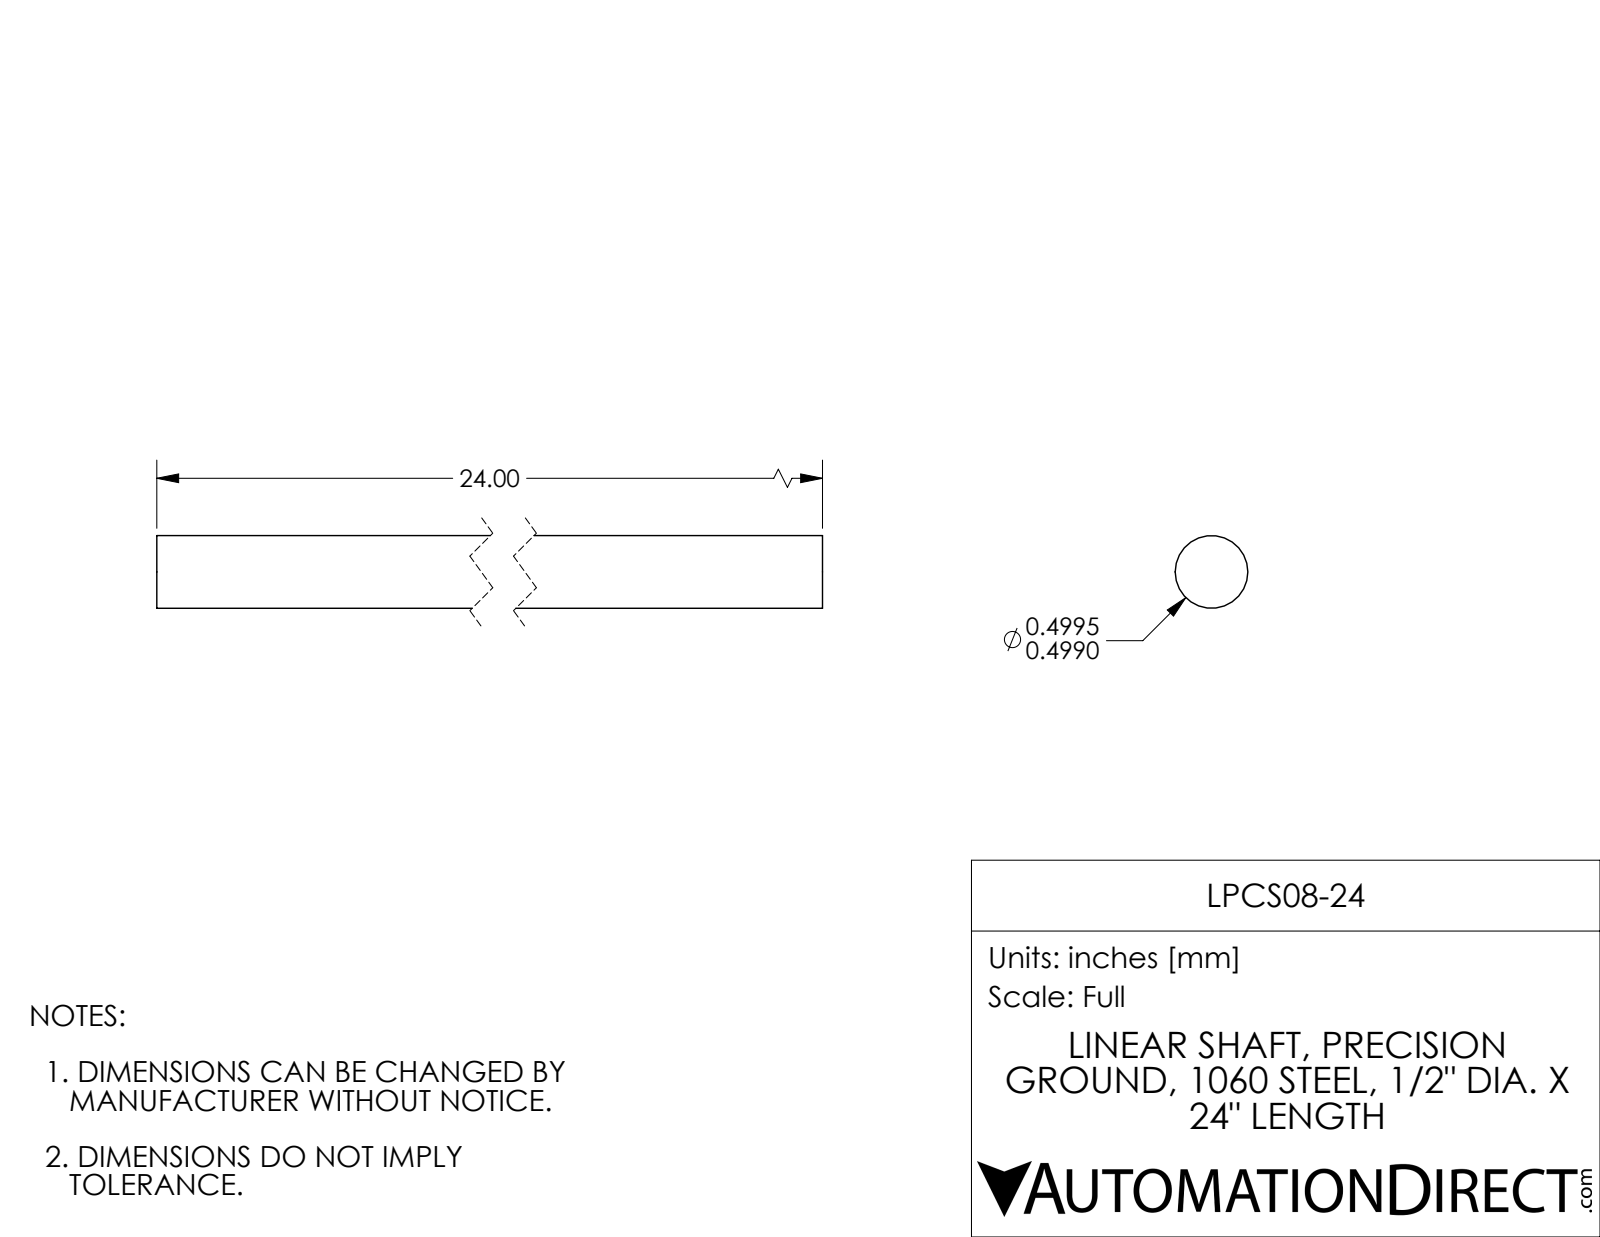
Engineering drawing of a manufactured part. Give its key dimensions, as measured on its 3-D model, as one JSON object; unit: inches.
{"part_name": "LPCS08-24", "step_written_by": "SolidWorks 2017 (AUTOMOTIVE_DESIGN)", "units": "inches", "bodies": {"solids": 1, "faces": 4, "planar": 2, "cylindrical": 2, "other": 0}, "overall_size": [24, 0.499, 0.499], "volume_in3": 4.703, "surface_area_in2": 38.05, "round_bosses_or_shafts": [[0.5, 1]], "face_to_face_distances": [24]}
